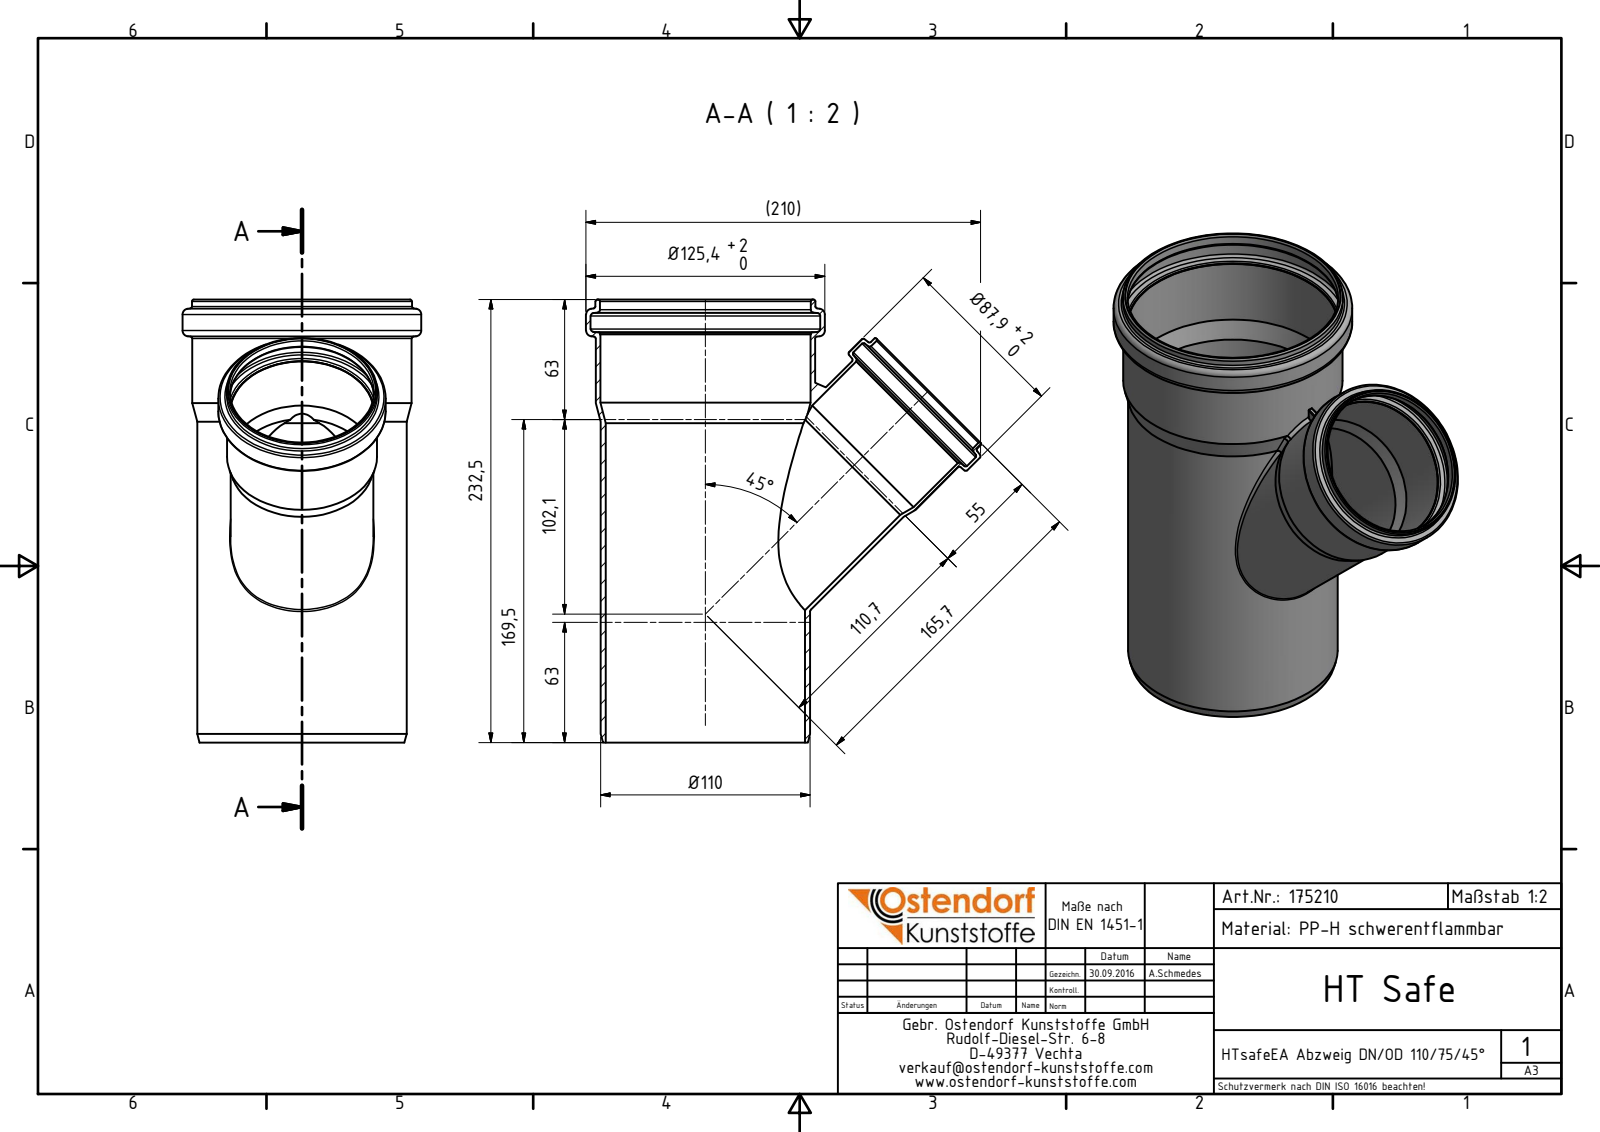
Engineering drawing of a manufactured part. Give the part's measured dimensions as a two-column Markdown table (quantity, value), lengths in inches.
| quantity | value |
| --- | --- |
| part name | 175210 HTsafeEA DN_OD 110_75_45° |
| STEP written by | Autodesk Inventor 2016 (AUTOMOTIVE_DESIGN) |
| units | inches |
| bodies | 1 solid, 68 faces (8 planar, 20 cylindrical, 40 other) |
| overall size | 9.154 × 8.174 × 4.937 |
| volume | 14.86 in³ |
| surface area | 316.4 in² |
| round holes (diameter × count) | 2.803 × 1, 2.969 × 1, 2.98 × 1, 3.327 × 1, 4.118 × 1, 4.346 × 1, 4.358 × 1, 4.748 × 1 |
| round bosses / shafts (diameter × count) | 4.937 × 1, 4.547 × 1, 4.535 × 1, 4.331 × 1, 3.461 × 1, 3.114 × 1, 3.102 × 1, 2.953 × 1 |
| partial cylindrical surfaces (radius × count) | 0.02 × 2 |
| main face-to-face distances | 9.154, 8.432, 0.721, 0.626, 0.106 |
